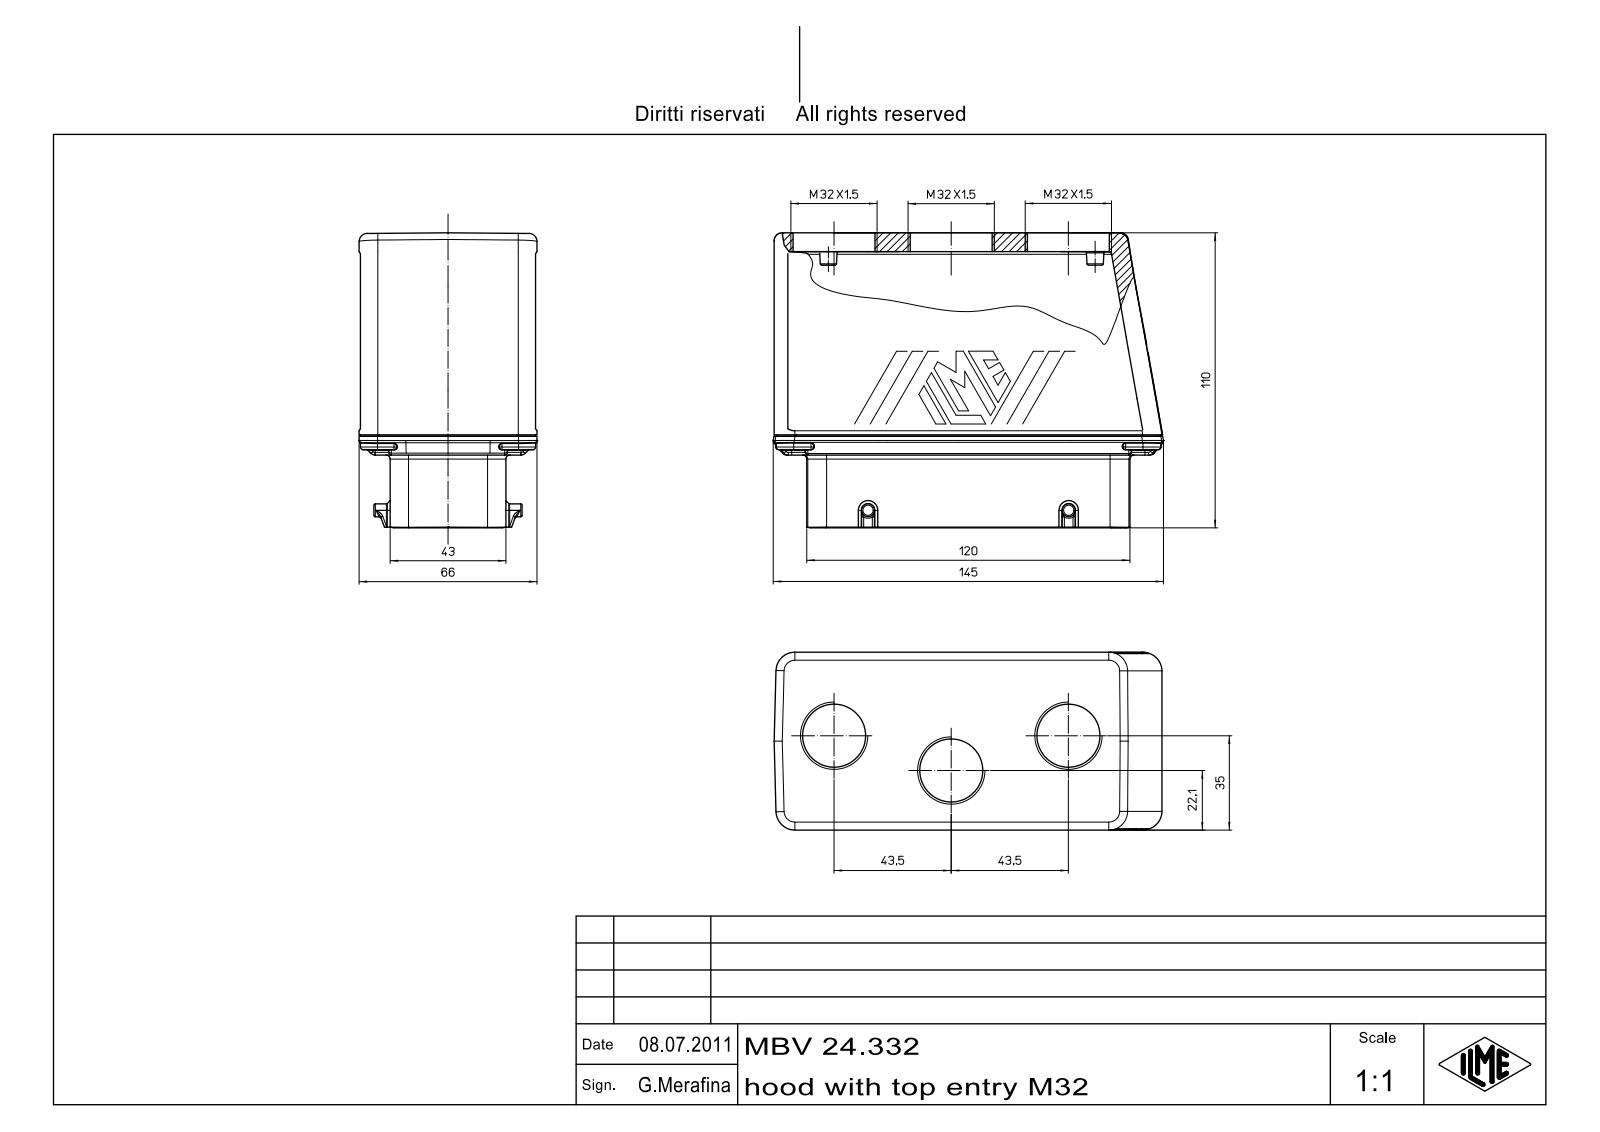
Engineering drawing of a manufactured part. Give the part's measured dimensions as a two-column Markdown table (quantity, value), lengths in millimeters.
| quantity | value |
| --- | --- |
| part name | 53848 |
| STEP written by | CoCreate Modeling 16.00A 16-Aug-2008 (C) Parametric Technology GmbH (AUTOMOTIVE_DESIGN) |
| units | millimeters |
| bodies | 1 solid, 696 faces (378 planar, 128 cylindrical, 190 other) |
| overall size | 143.75 × 108.97 × 66.01 |
| volume | 684 771 mm³ |
| surface area | 76 642 mm² |
| round holes (diameter × count) | 32 × 3 |
| round bosses / shafts (diameter × count) | 4.8 × 2 |
| partial cylindrical surfaces (radius × count) | 1 × 44, 7 × 12, 0.5 × 8, 0.3 × 6, 1.5 × 6, 3 × 6, 4.2 × 4, 5 × 4 |
| main face-to-face distances | 65.01, 82.21, 0.4, 65.41, 11, 54.01, 54, 43, 11.01, 52.21 |
| hole center spacings | 45.37, 45.39, 87 |
